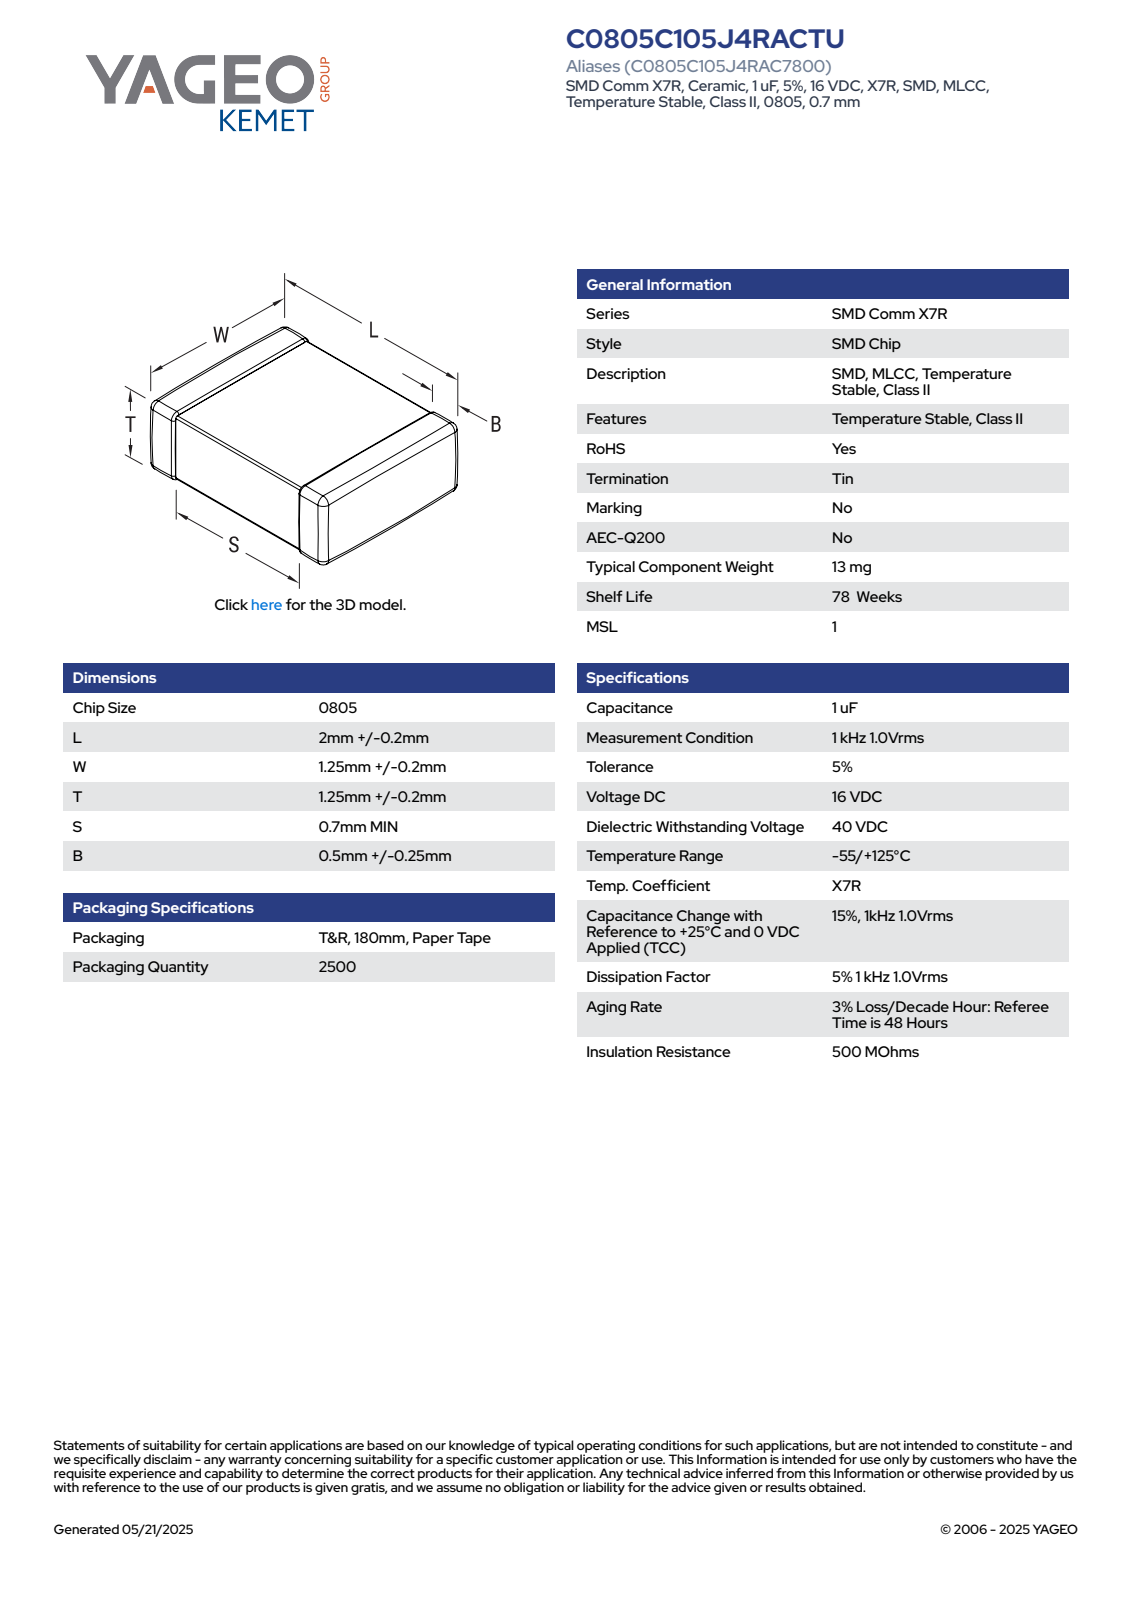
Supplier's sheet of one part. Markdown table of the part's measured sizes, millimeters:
| quantity | value |
| --- | --- |
| part name | CCS_CCSTD_0805_L2.2W1.45T1.45B0.5 |
| STEP written by | SolidWorks 2014 (AUTOMOTIVE_DESIGN) |
| units | millimeters |
| bodies | 4 solids, 125 faces (71 planar, 38 cylindrical, 16 other) |
| overall size | 2.2 × 1.45 × 1.45 |
| volume | 4 mm³ |
| surface area | 17 mm² |
| main face-to-face distances | 1.42, 1.39, 1.45, 2.2, 0.97, 1.23, 1.19, 1.01, 0.58, 0.87 |
